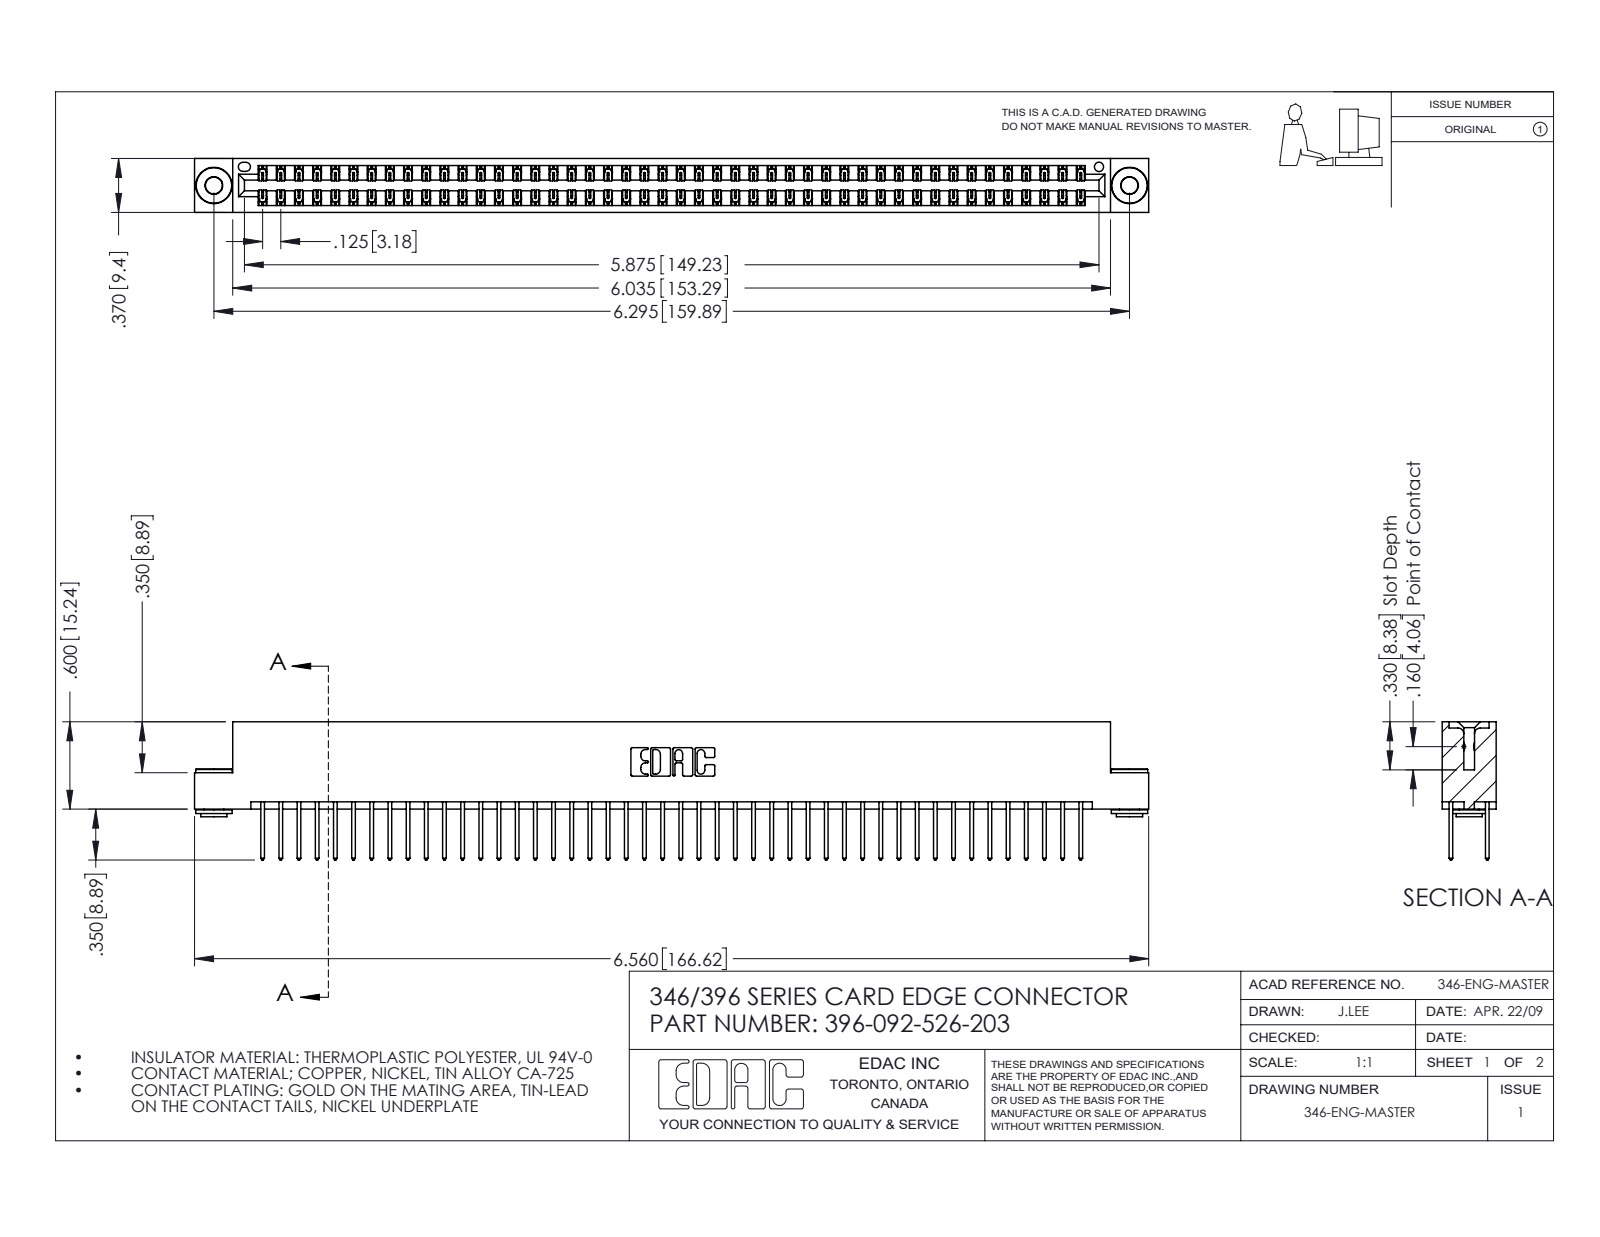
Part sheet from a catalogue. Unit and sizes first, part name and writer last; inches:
Units: inches
Overall size (bounding box): 6.56 × 0.95 × 0.37
Round holes (diameter × count): ⌀0.116 ×2, ⌀0.156 ×2, ⌀0.064 ×1
Round bosses / shafts (diameter × count): ⌀0.25 ×2, ⌀0.18 ×2, ⌀0.136 ×2
Partial cylindrical surfaces — rounded edges, fillets, slot ends (radius × count): R0.006 ×138, R0.01 ×92, R0.01 ×22, R0.007 ×6, R0.031 ×6, R0.026 ×3, R0.014 ×2, R0.022 ×2
Main face-to-face distances: 0.048, 0.322, 0.25, 0.37, 0.025, 0.072, 0.298, 0.275, 0.148, 0.222
Hole centre spacings: 0.246, 6.086, 6.295
Volume: 1.004 in³ · Surface area: 36.52 in²
Bodies: 95 solids, 4944 faces (3306 planar, 1630 cylindrical, 8 other)
Part name (STEP PRODUCT): 396-092-526-203; 345-292-001_345-293-126; 345-250-002_345-250-002-102; 346 Part_Flush Mounting Lugs - 0.156 Dia-TH
STEP written by: SolidWorks 2016 (CONFIG_CONTROL_DESIGN)
